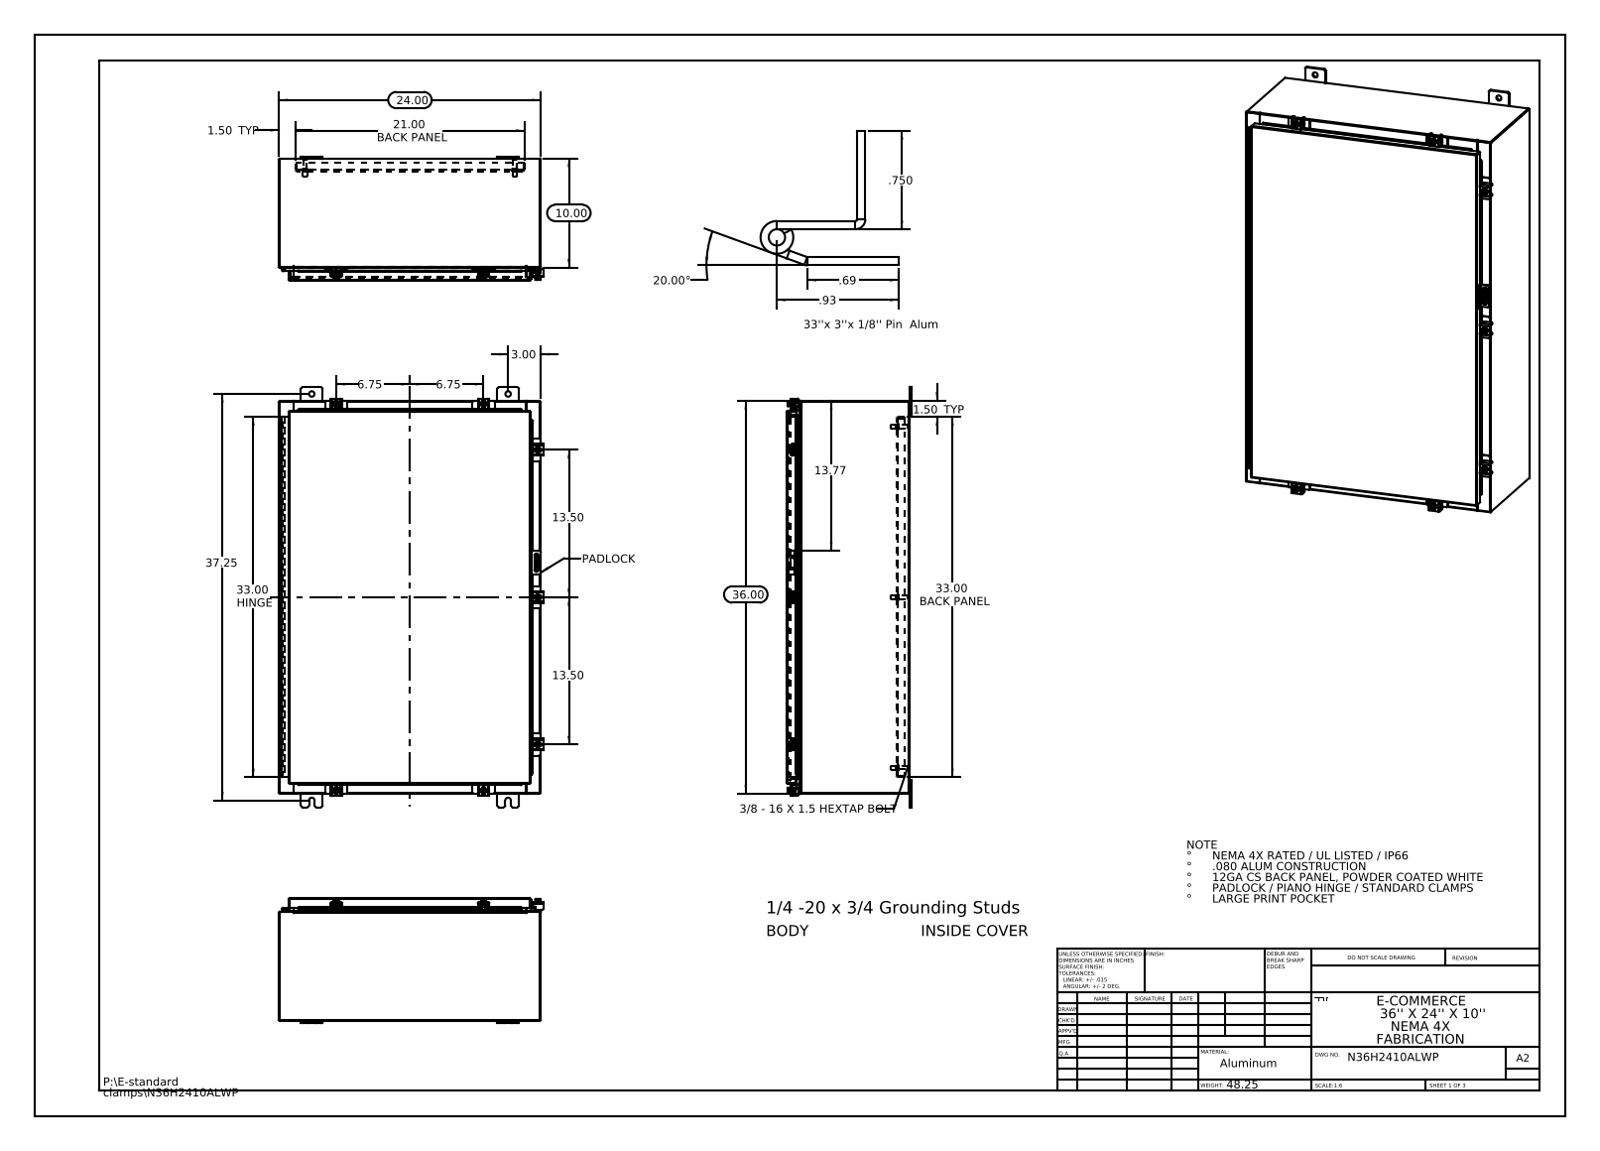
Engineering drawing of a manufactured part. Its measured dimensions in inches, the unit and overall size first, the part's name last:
Units: inches
Overall size (bounding box): 38.5 × 24.211 × 11.389
Round holes (diameter × count): ⌀0.5 ×10, ⌀0.213 ×7, ⌀0.26 ×7, ⌀0.125 ×2, ⌀0.125 ×1
Round bosses / shafts (diameter × count): ⌀0.25 ×8, ⌀0.5 ×7, ⌀0.399 ×7, ⌀0.625 ×6, ⌀0.375 ×6, ⌀0.33 ×6
Partial cylindrical surfaces — rounded edges, fillets, slot ends (radius × count): R0.06 ×34, R0.013 ×27, R0.19 ×24, R0.088 ×21, R0.12 ×14, R0.141 ×14, R0.05 ×11, R0.08 ×10
Main face-to-face distances: 0.075, 11.126, 11.201, 11.051, 0.104, 23.925, 1, 1.075, 10.051, 10.126
Hole centre spacings: 13.5, 15.625, 17.957, 24.793, 33.474, 37.154, 19.25, 1.858
Volume: 328.4 in³ · Surface area: 8 226 in²
Bodies: 54 solids, 2184 faces (1138 planar, 922 cylindrical, 124 other)
Part name (STEP PRODUCT): N36H2410ALWP 22104005_DEFAULT; N36H2410ALWP 22101002; N36H2410ALWP Clamp Bracket; N36H2410ALWP Padlock Hasp (+8 more)
STEP written by: SolidWorks 2013 (CONFIG_CONTROL_DESIGN)
